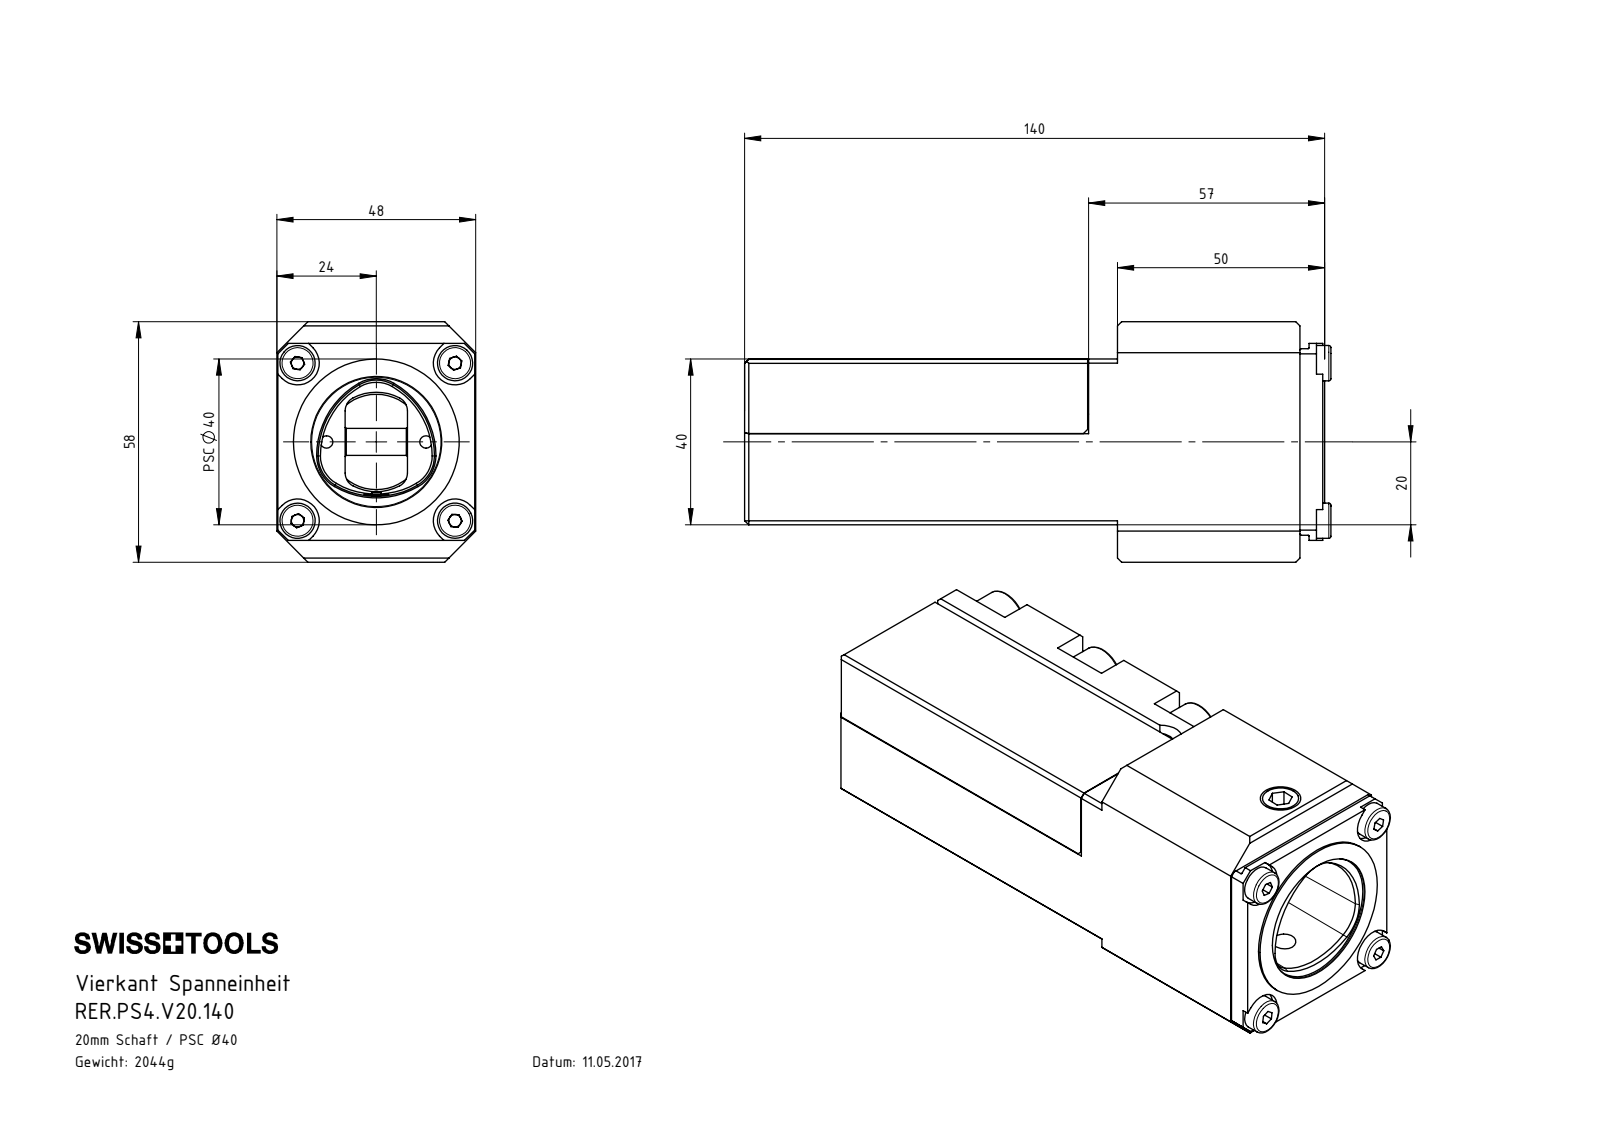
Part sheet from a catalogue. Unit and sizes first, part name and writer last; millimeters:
Units: millimetres
Overall size (bounding box): 141.5 × 58 × 48
Round holes (diameter × count): ⌀4.2 ×4, ⌀5.5 ×4, ⌀2.5 ×3, ⌀6.8 ×3, ⌀9 ×3, ⌀3 ×2, ⌀3.3 ×2, ⌀4 ×1, ⌀6 ×1, ⌀7 ×1, ⌀8.57 ×1, ⌀10.2 ×1
Round bosses / shafts (diameter × count): ⌀8.5 ×4, ⌀8 ×4, ⌀5 ×4, ⌀13 ×3, ⌀5.5 ×2, ⌀3 ×2, ⌀40 ×1, ⌀39.7 ×1
Partial cylindrical surfaces — rounded edges, fillets, slot ends (radius × count): R3.5 ×4, R5.25 ×4, R7.5 ×3, R0.2 ×2, R2.75 ×2, R3 ×2, R9 ×1, R12 ×1
Main face-to-face distances: 48, 9, 39.93, 49, 2, 134, 42, 47.89, 48.93, 58
Hole centre spacings: 33, 20.25, 26.87, 36.36, 38, 66, 12, 12.69
Volume: 269 599 mm³ · Surface area: 76 056 mm²
Bodies: 23 solids, 788 faces (345 planar, 172 cylindrical, 271 other)
Part name (STEP PRODUCT): DIN 6325_ø3x10_2x6; DIN 3771 - 38x1.5; U40-PS4.023.006_D; ISO 4762 - M8 x 35 (+8 more)
STEP written by: SolidWorks 2022 (AUTOMOTIVE_DESIGN)
